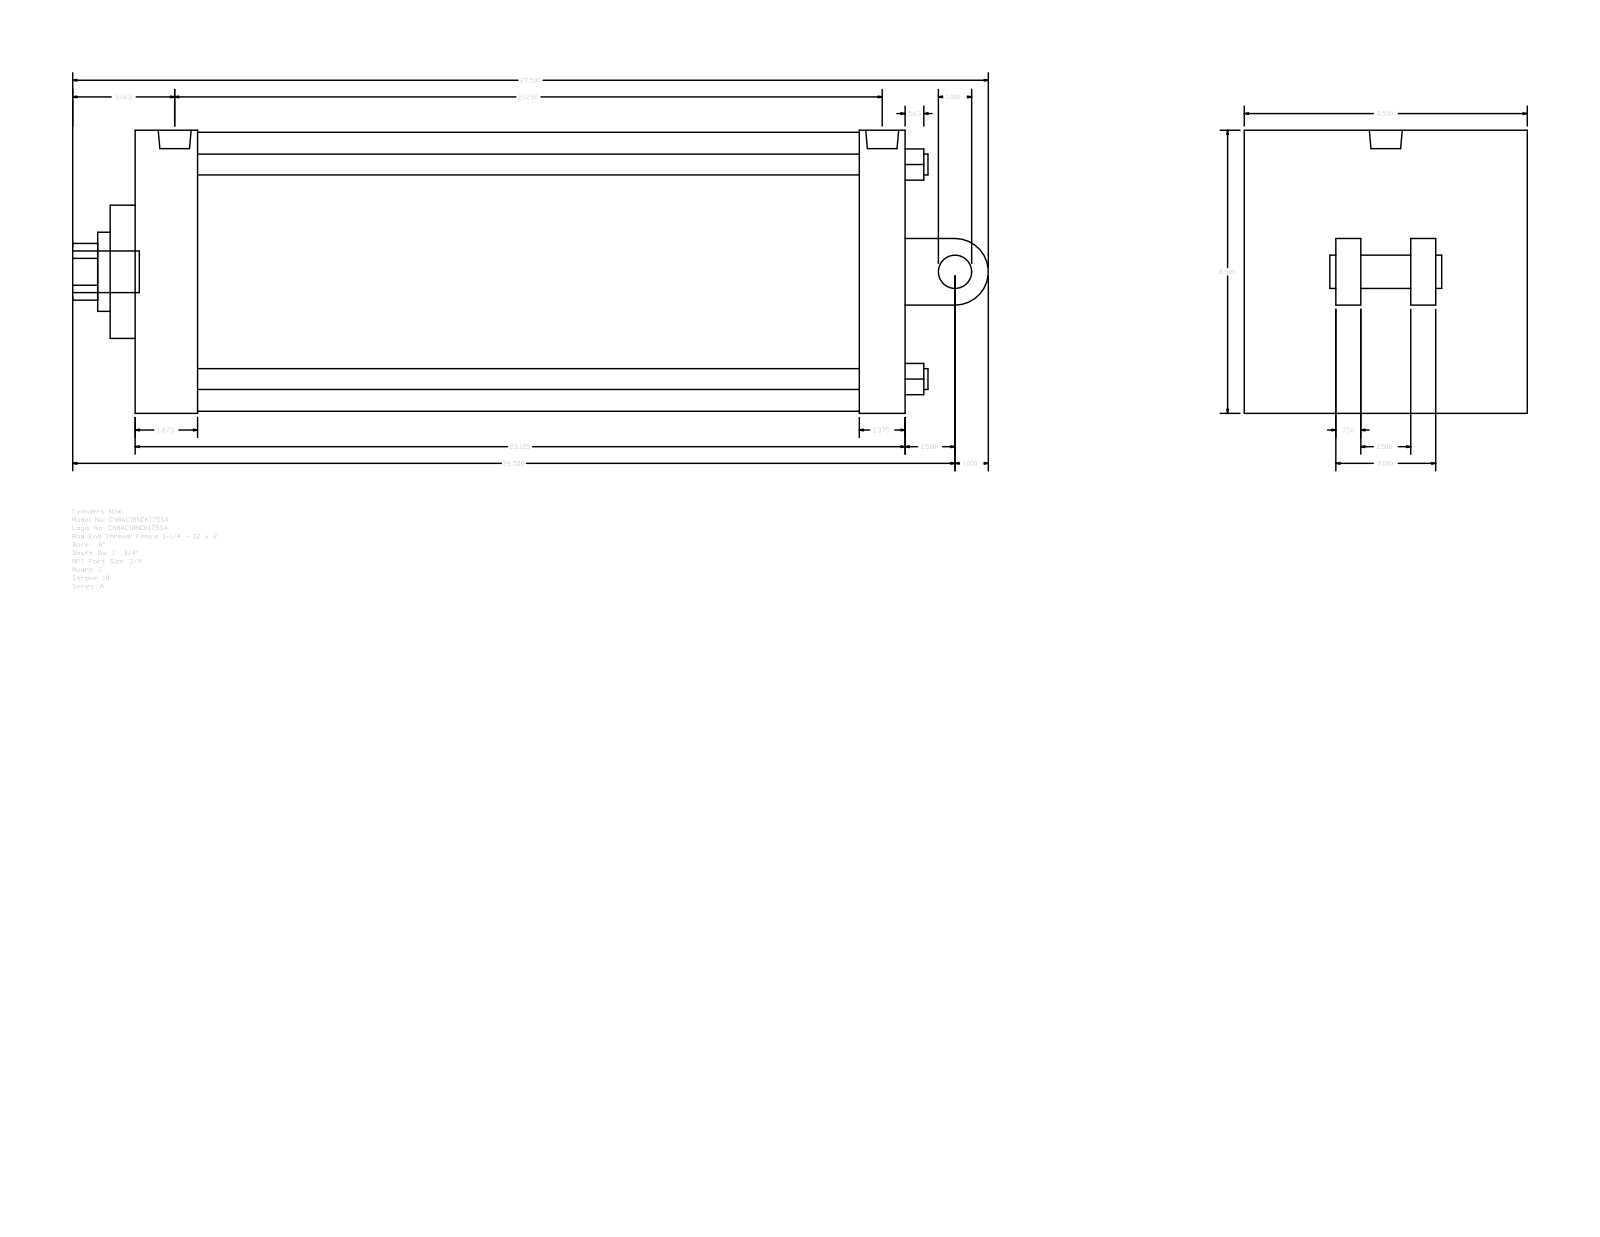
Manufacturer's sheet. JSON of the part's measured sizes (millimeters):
{"part_name": "A_C__0800_1.75", "step_written_by": "GSSL Pune (CONFIG_CONTROL_DESIGN)", "units": "millimeters", "bodies": {"solids": 0, "faces": 104, "planar": 75, "cylindrical": 29, "other": 0}, "overall_size": [698.5, 215.9, 215.9], "round_holes": [[15.88, 4], [15.08, 2], [25.12, 1], [44.45, 1], [60.33, 1], [212.72, 1]], "round_bosses_or_shafts": [[15.08, 2], [31.75, 1], [25.4, 1], [25.12, 1]], "partial_cylinders_radius": [[21.63, 1], [25.4, 1]], "face_to_face_distances": [587.38, 215.9, 19.05, 57.15, 34.92, 47.63, 539.75, 552.46, 504.83, 88.9], "hole_center_spacings": [115.67, 163.58, 231.34, 6.35]}
